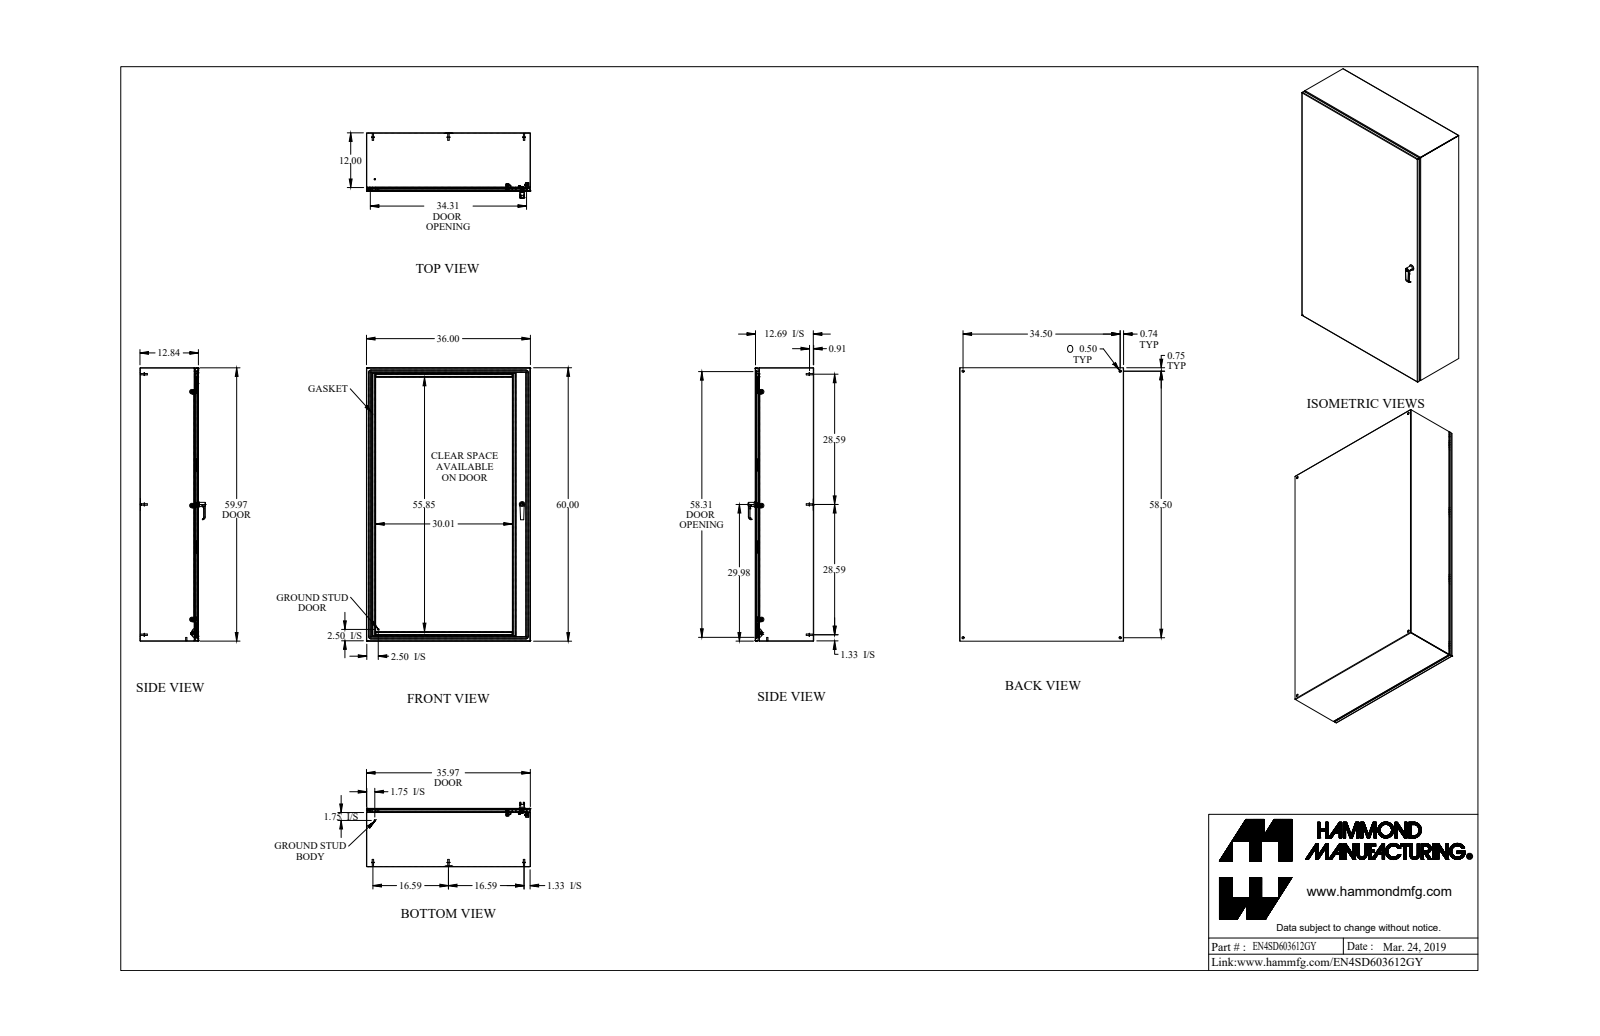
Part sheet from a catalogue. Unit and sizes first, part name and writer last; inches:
Units: inches
Overall size (bounding box): 60 × 36 × 14.367
Round holes (diameter × count): ⌀0.176 ×6, ⌀0.196 ×4, ⌀0.5 ×4, ⌀0.25 ×3, ⌀0.265 ×3, ⌀0.413 ×3, ⌀0.256 ×2, ⌀0.313 ×2, ⌀0.394 ×2, ⌀0.172 ×1, ⌀0.24 ×1, ⌀0.242 ×1
Round bosses / shafts (diameter × count): ⌀0.313 ×8, ⌀0.27 ×8, ⌀0.25 ×7, ⌀0.625 ×6, ⌀0.375 ×6, ⌀0.156 ×6, ⌀1 ×3, ⌀0.625 ×3
Partial cylindrical surfaces — rounded edges, fillets, slot ends (radius × count): R0.043 ×24, R0.036 ×18, R0.108 ×18, R0.062 ×17, R0.03 ×15, R0.094 ×10, R0.016 ×9, R0.006 ×8
Main face-to-face distances: 0.072, 12.765, 12.693, 12.837, 35.928, 35.856, 36, 0.072, 59.856, 59.928
Hole centre spacings: 0.786, 49.969, 24.981, 24.988, 25, 34.5, 58.5, 67.915
Volume: 552.2 in³ · Surface area: 15 578 in²
Bodies: 63 solids, 1715 faces (757 planar, 636 cylindrical, 322 other)
Part name (STEP PRODUCT): EN4SD603612GY
STEP written by: SolidWorks 2018 (AUTOMOTIVE_DESIGN)
